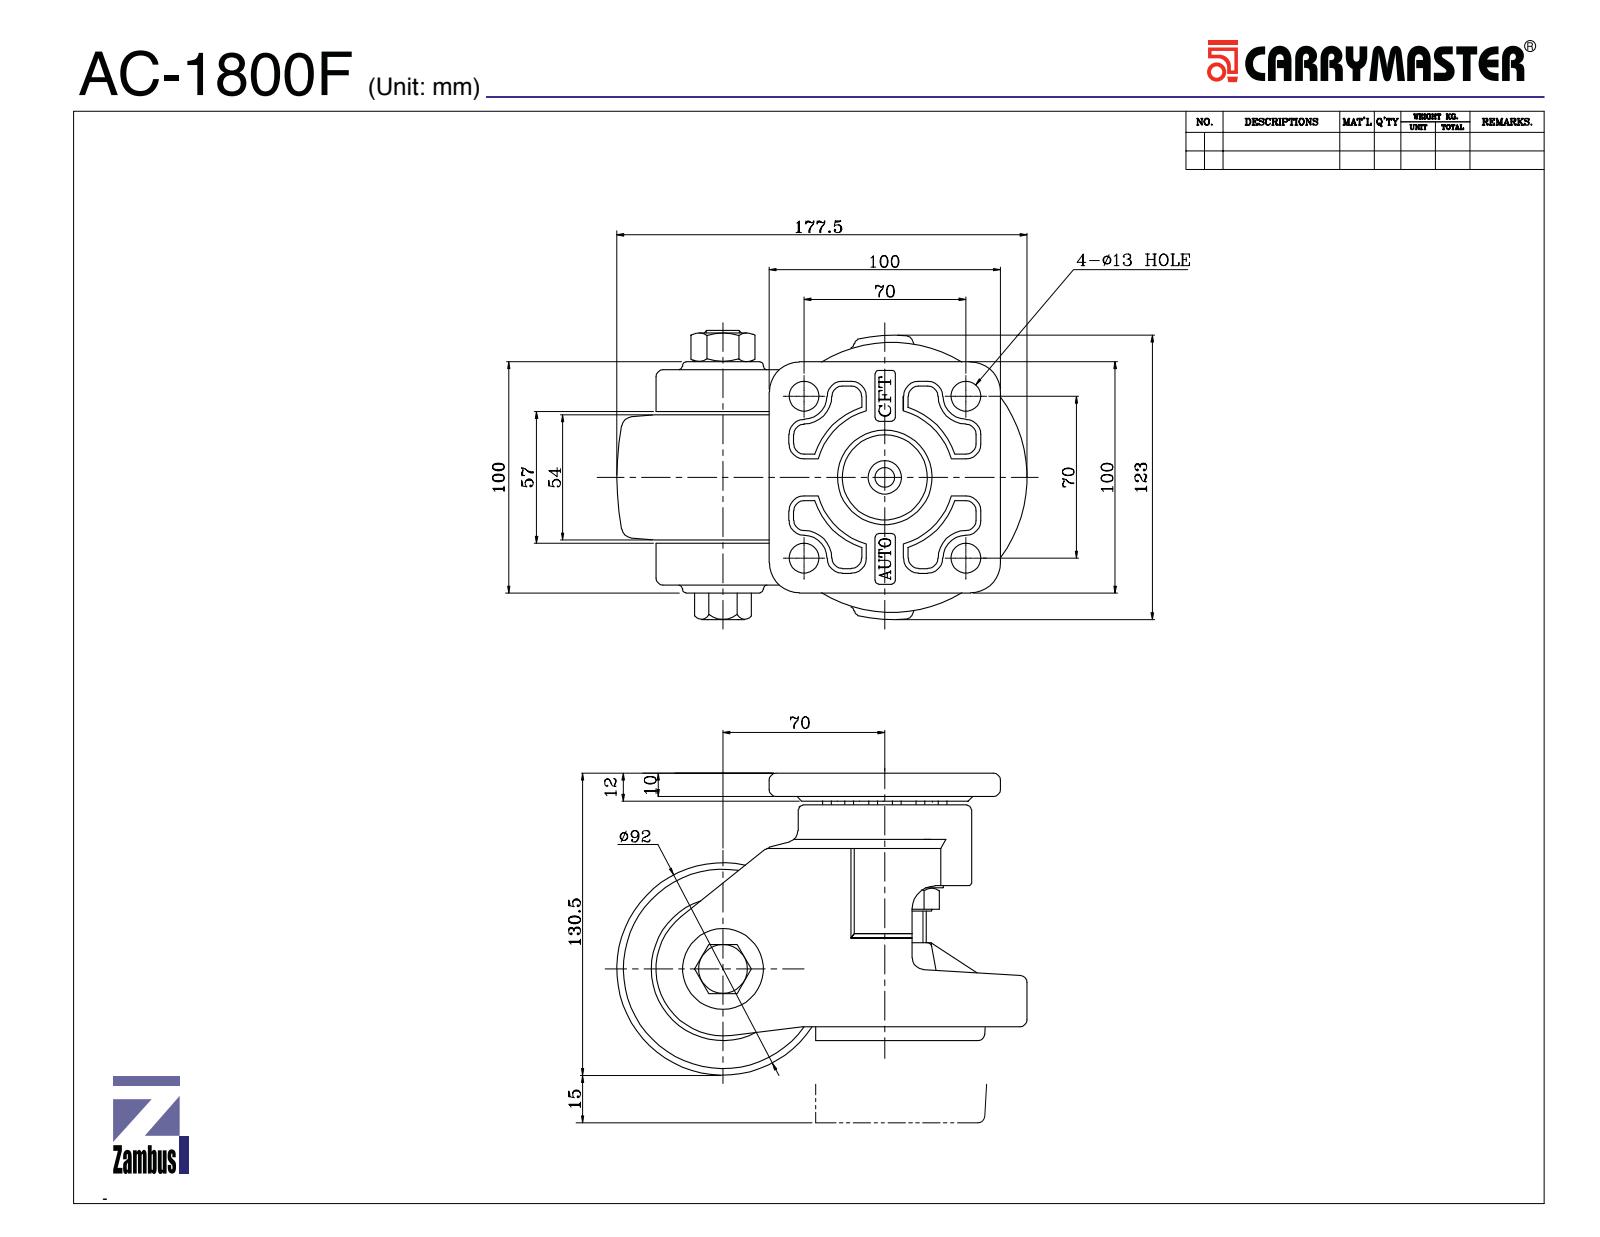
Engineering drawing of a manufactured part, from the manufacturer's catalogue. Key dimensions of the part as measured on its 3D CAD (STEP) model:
Part name (STEP PRODUCT): AC-1800F
STEP written by: SolidWorks 2015 (CONFIG_CONTROL_DESIGN)
Units: millimetres
Bodies: 27 solids, 2362 faces (467 planar, 261 cylindrical, 1634 other)
Overall size (bounding box): 177.5 × 130.5 × 123.5
Volume: 1 129 000 mm³ · Surface area: 199 411 mm²
Round holes (diameter × count): ⌀13 ×4, ⌀6.8 ×1, ⌀8.5 ×1, ⌀14.3 ×1, ⌀14.5 ×1, ⌀17.5 ×1, ⌀18 ×1, ⌀18.5 ×1, ⌀25 ×1, ⌀26.5 ×1, ⌀34 ×1, ⌀54 ×1
Round bosses / shafts (diameter × count): ⌀35 ×2, ⌀20 ×2, ⌀92 ×1, ⌀74 ×1, ⌀50 ×1, ⌀36 ×1, ⌀30 ×1, ⌀25.8 ×1
Partial cylindrical surfaces — rounded edges, fillets, slot ends (radius × count): R3 ×24, R0.5 ×18, R5 ×17, R1.5 ×16, R2 ×10, R13 ×4, R10 ×2, R9 ×1
Main face-to-face distances: 1.5, 10, 18, 55.5, 19.5, 73.5, 75, 57, 20, 12
Hole centre spacings: 49.5, 70, 98.99
